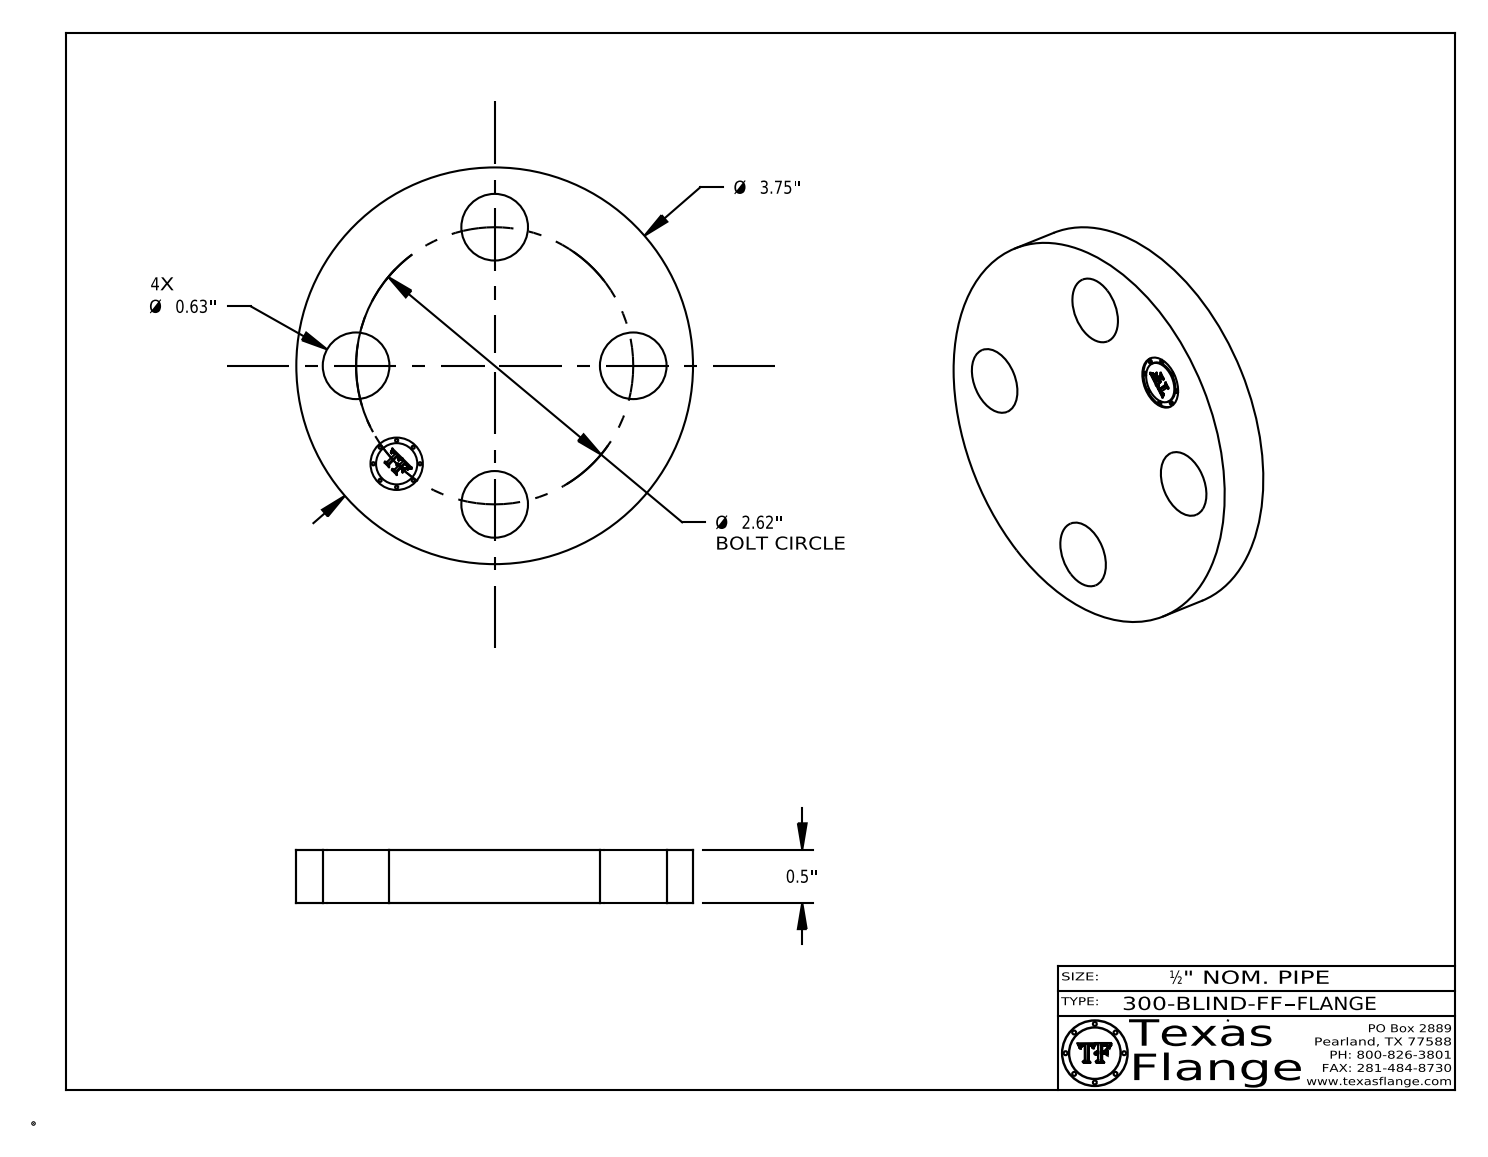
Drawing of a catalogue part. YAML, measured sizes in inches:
part_name: "300-BLIND-FF"
step_written_by: "CATIA V5 STEP AP214 (AUTOMOTIVE_DESIGN)"
units: inches
bodies: {solids: 1, faces: 397, planar: 367, cylindrical: 30, other: 0}
overall_size: [3.75, 3.75, 0.5]
volume: 4.898
surface_area: 29.54
round_holes:
  - {diameter: 0.63, count: 4}
  - {diameter: 0.495, count: 1}
round_bosses_or_shafts:
  - {diameter: 0.03, count: 8}
  - {diameter: 3.75, count: 1}
  - {diameter: 0.39, count: 1}
face_to_face_distances: [0.5, 0.485, 0.015, 0.148, 0.144, 0.027, 0.096, 0.122, 0.021, 0.074]
hole_center_spacings: [1.852, 1.003, 2.42, 2.62]
